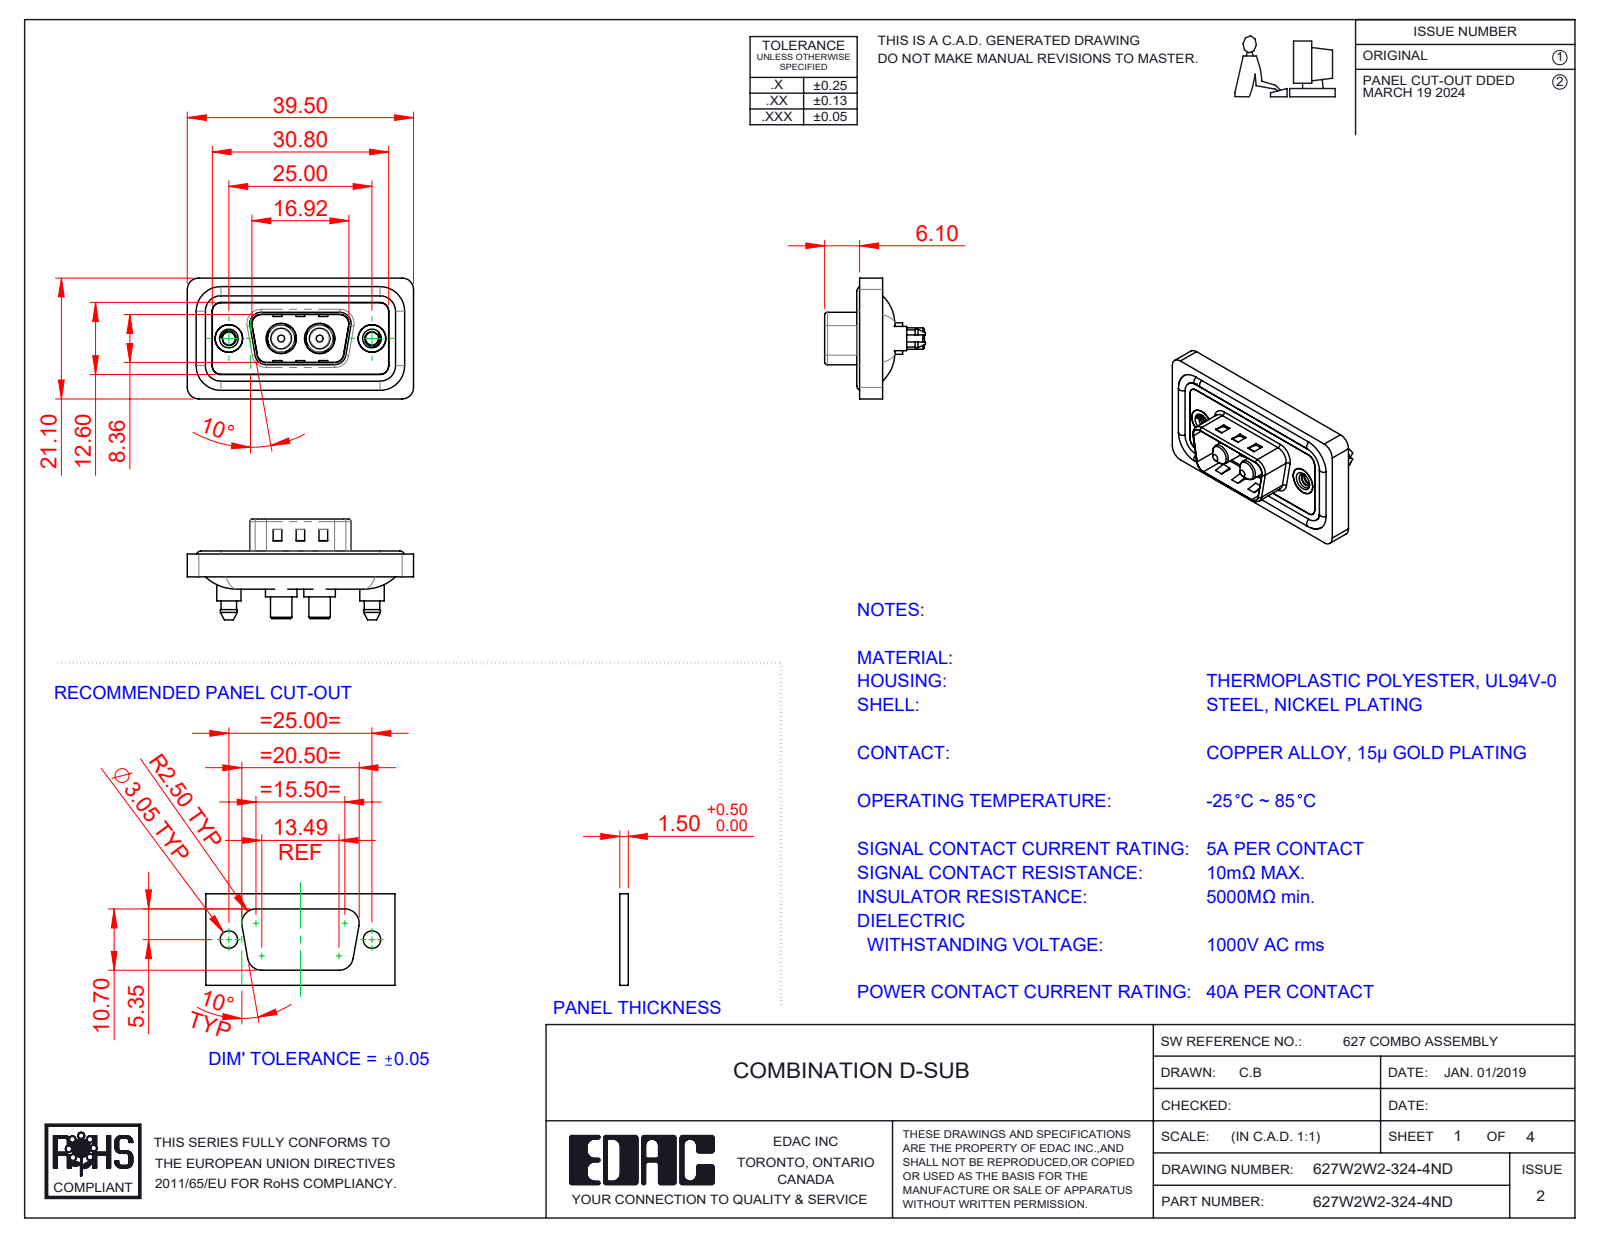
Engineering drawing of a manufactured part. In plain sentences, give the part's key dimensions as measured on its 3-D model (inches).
The part is named "627W2W2-324-4ND; Power Pin_40A S; 627Combo Waterproof Housing_09 Contacts; 627Combo Housing_2W2 (+4 more)". Its 3-D file was written by "SolidWorks 2023 (CONFIG_CONTROL_DESIGN)". It is 11 solids with 547 faces: 181 planar, 258 cylindrical and 108 other. Overall it measures 1.555 by 0.831 by 0.693 inches. Its volume is 0.283 cubic inches and its surface area 11.38 square inches. Round holes: 2 of diameter 0.089, 2 of diameter 0.157, 2 of diameter 0.189, 2 of diameter 0.191, 2 of diameter 0.197, 2 of diameter 0.209. Round bosses or shafts: 4 of diameter 0.063, 2 of diameter 0.217, 2 of diameter 0.213, 2 of diameter 0.205, 2 of diameter 0.193, 2 of diameter 0.187, 2 of diameter 0.167, 2 of diameter 0.148. Partial cylindrical surfaces (rounded edges, fillets, slot ends): 24 of radius 0.059, 18 of radius 0.079, 10 of radius 0.063, 8 of radius 0.02, 4 of radius 0.01, 4 of radius 0.024, 4 of radius 0.026, 4 of radius 0.035. The main face-to-face distances are 0.016, 0.043, 0.114, 0.122, 0.02, 0.063, 0.059, 0.157, 0.028, 0.098. The hole center spacings are 0.36, 0.624, 0.265, 0.984.
